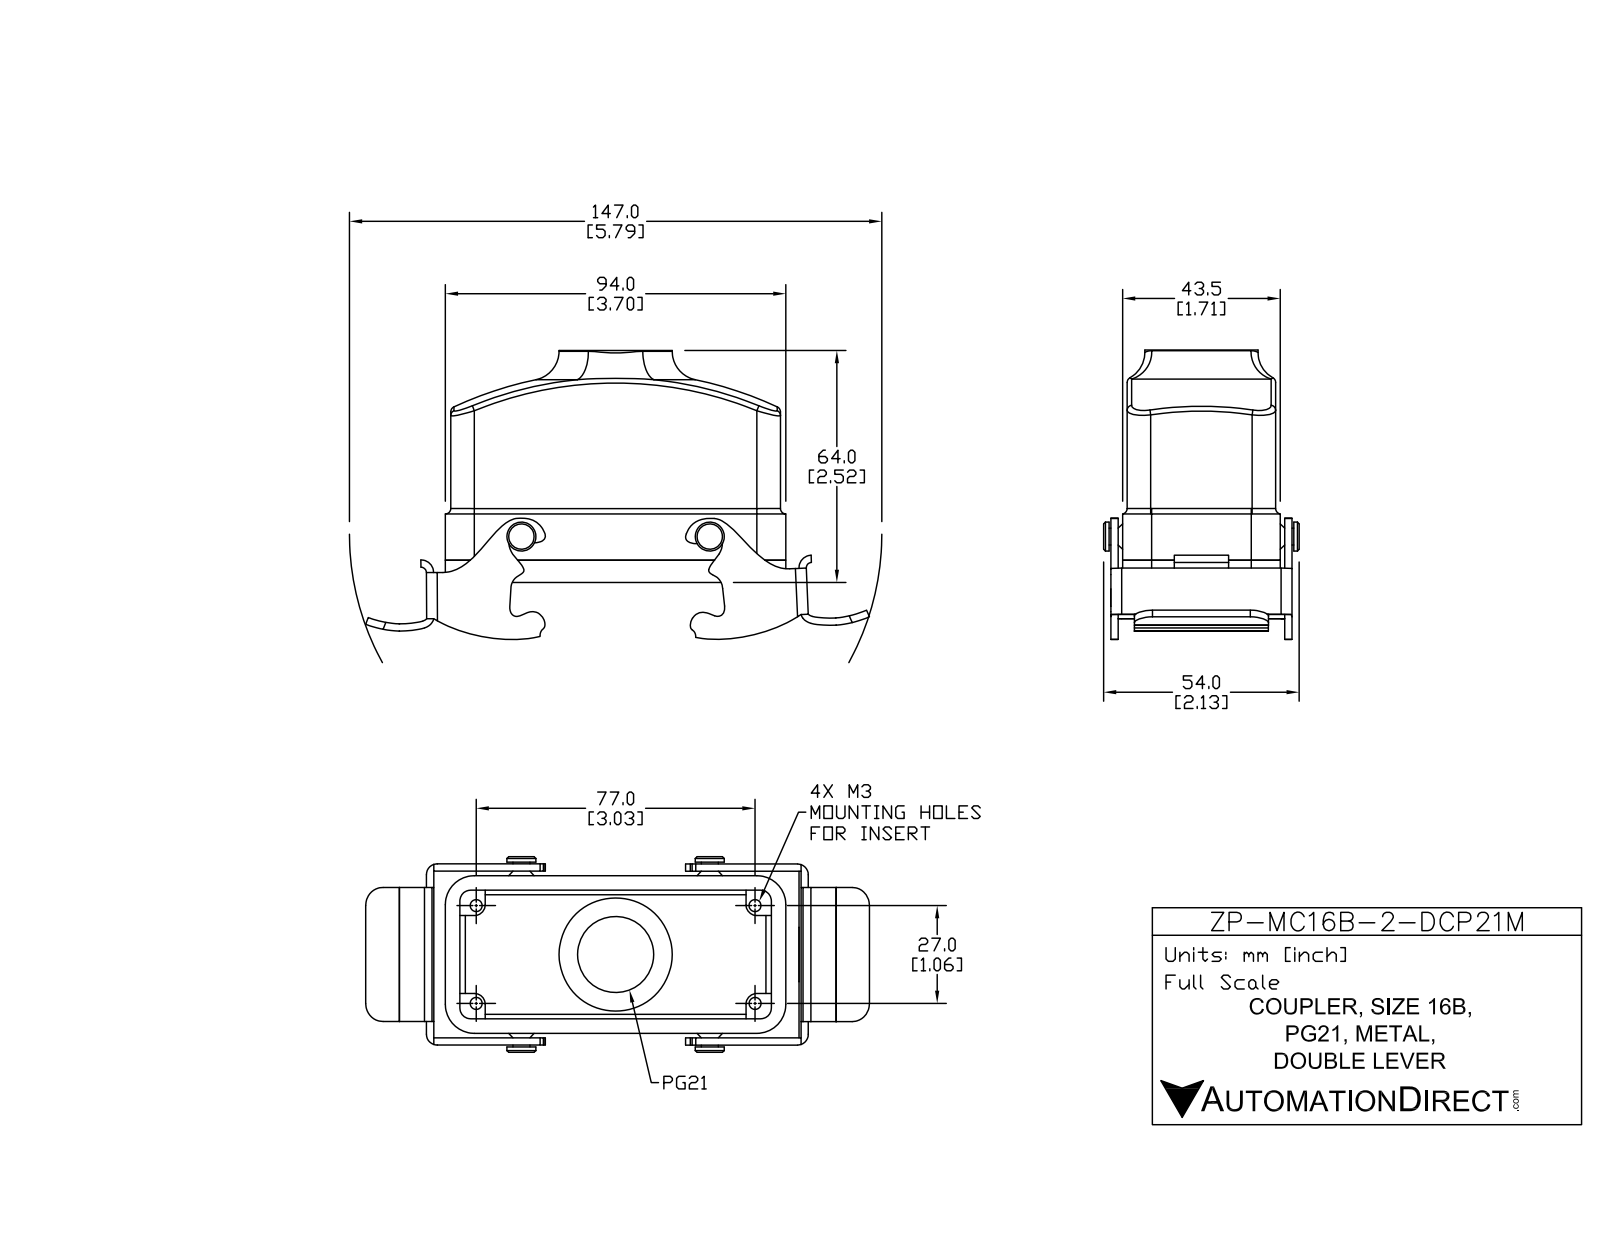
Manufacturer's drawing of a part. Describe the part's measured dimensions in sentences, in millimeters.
The part is named "ZP-MC16B-2-DCP21M". Its 3-D file was written by "SolidWorks 2011 (AUTOMOTIVE_DESIGN)". It is 8 solids with 319 faces: 128 planar, 152 cylindrical and 39 other. Overall it measures 128.64 by 76.52 by 54 millimeters. Its volume is 72 840 cubic millimeters and its surface area 47 712 square millimeters. Round holes: 4 of diameter 3.3, 1 of diameter 21, 1 of diameter 26. Round bosses or shafts: 2 of diameter 8, 2 of diameter 4.67, 1 of diameter 31.25. Partial cylindrical surfaces (rounded edges, fillets, slot ends): 16 of radius 1, 14 of radius 3, 10 of radius 0.5, 6 of radius 2, 4 of radius 1.5, 4 of radius 5.5, 4 of radius 6.5, 4 of radius 8. The main face-to-face distances are 4, 1.25, 38.25, 5.25, 39.5, 37, 43.5, 1, 2.5, 42.25. The hole center spacings are 40.95, 26.5, 77.5, 81.91.
